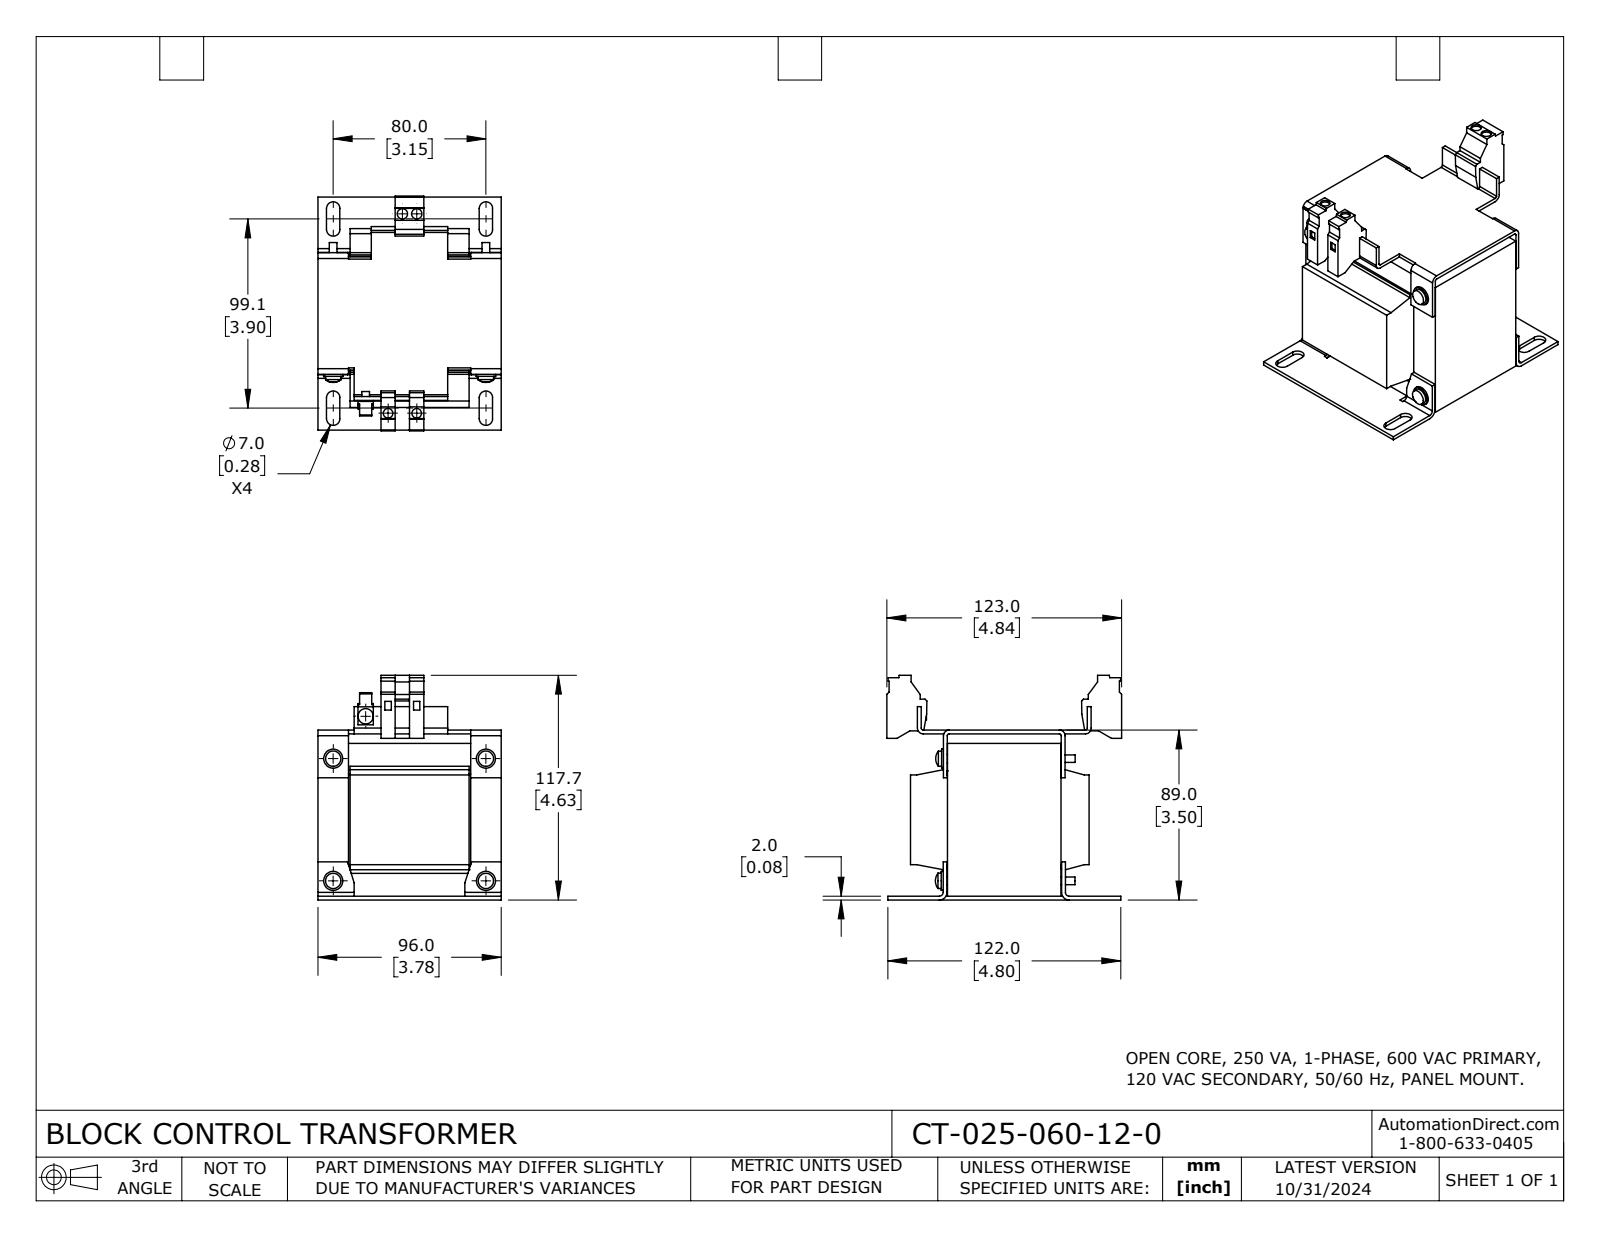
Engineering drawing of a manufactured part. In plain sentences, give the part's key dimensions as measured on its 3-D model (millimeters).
The part is named "CT-025-060-12-0". Its 3-D file was written by "SolidWorks 2023 (CONFIG_CONTROL_DESIGN)". It is 1 solid with 330 faces: 241 planar, 85 cylindrical and 4 other. Overall it measures 123 by 117.7 by 96 millimeters. Its volume is 612 400 cubic millimeters and its surface area 105 600 square millimeters. Round holes: 2 of diameter 5, 2 of diameter 5.4. Round bosses or shafts: 5 of diameter 8, 5 of diameter 4, 4 of diameter 10, 4 of diameter 4.5. Partial cylindrical surfaces (rounded edges, fillets, slot ends): 8 of radius 3.5, 4 of radius 1, 4 of radius 3, 2 of radius 2, 2 of radius 4. The main face-to-face distances are 2, 87, 80, 16, 16.8, 79.2, 64, 89, 85, 5. The hole center spacings are 104.7, 7.5, 15, 104.4, 105.5.
